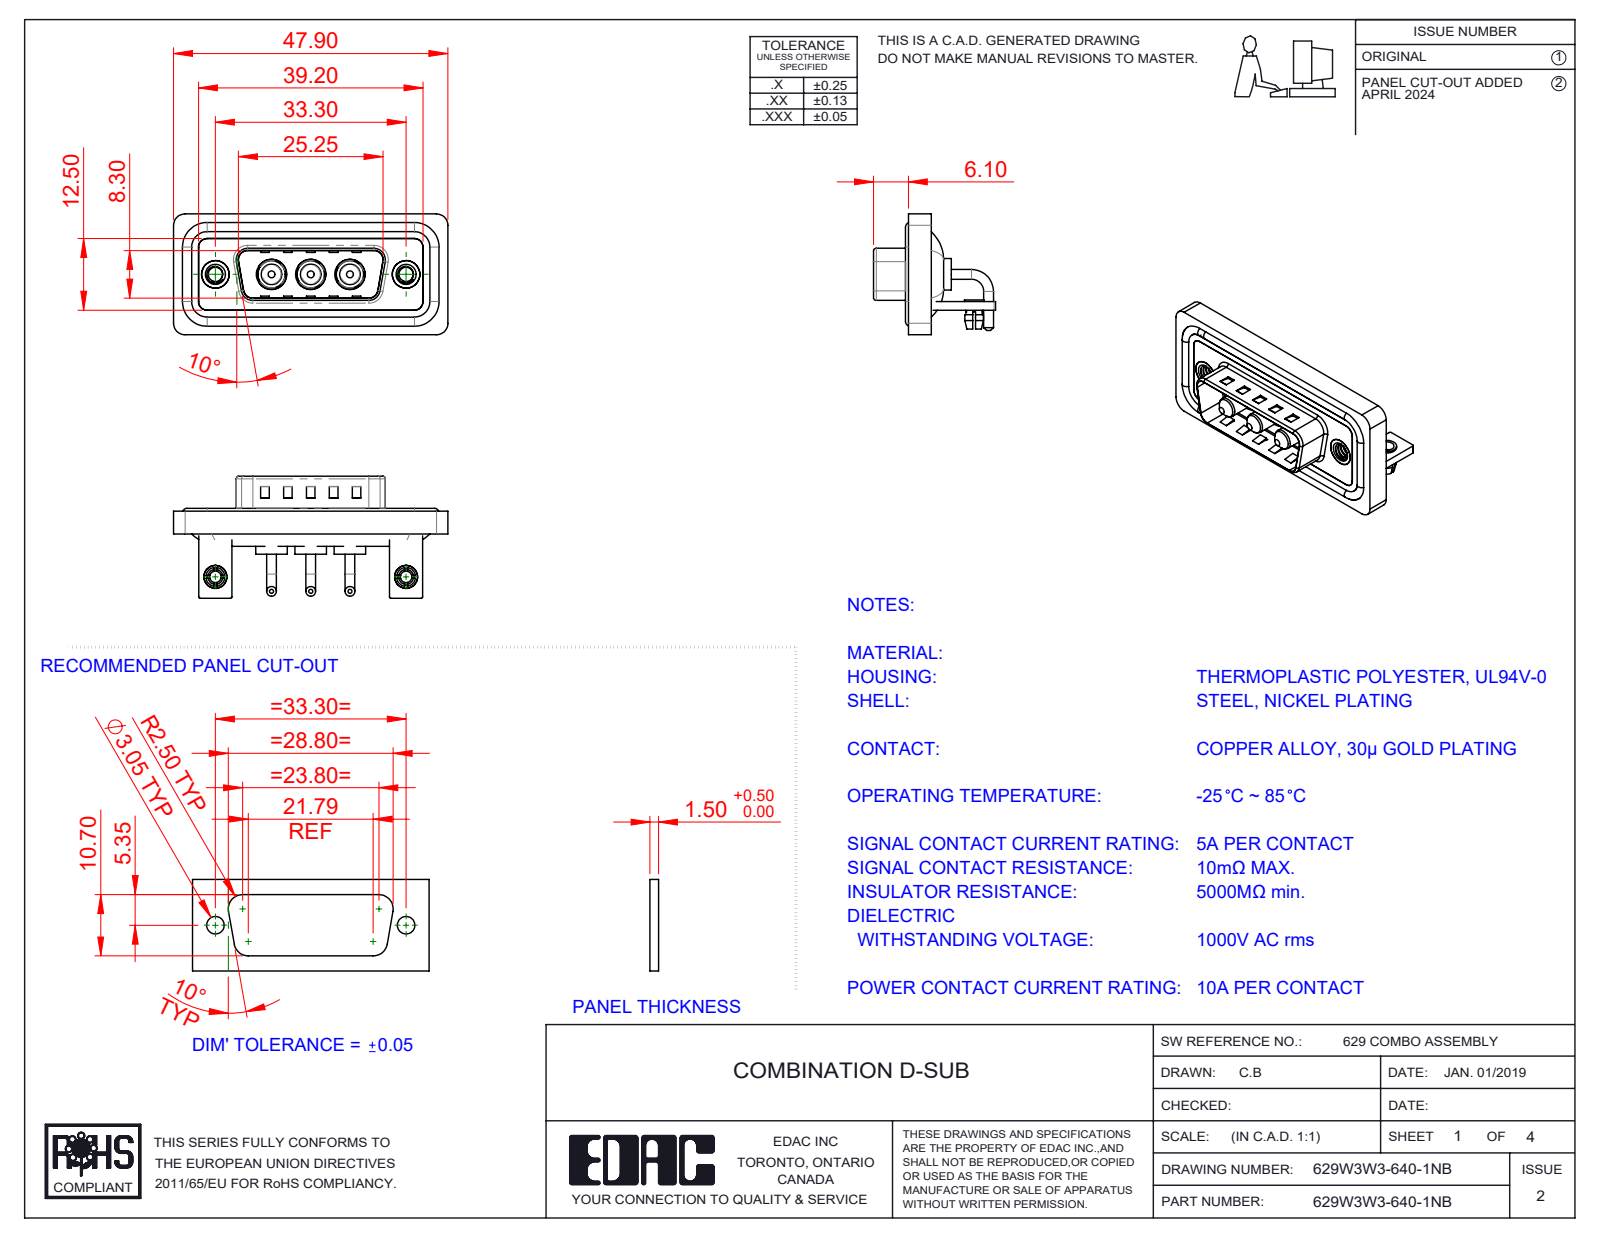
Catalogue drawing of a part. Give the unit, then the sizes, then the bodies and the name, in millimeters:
Units: millimetres
Overall size (bounding box): 47.9 × 21.3 × 21.1
Round holes (diameter × count): ⌀2.5 ×4, ⌀4.85 ×3, ⌀5.3 ×3, ⌀2 ×2, ⌀3.2 ×2, ⌀4 ×2, ⌀4.8 ×2, ⌀5 ×2
Round bosses / shafts (diameter × count): ⌀1.7 ×6, ⌀1.6 ×4, ⌀5.5 ×3, ⌀5.2 ×3, ⌀4.75 ×3, ⌀3.75 ×3, ⌀3.6 ×3, ⌀4.9 ×2
Partial cylindrical surfaces — rounded edges, fillets, slot ends (radius × count): R2 ×21, R1.5 ×18, R0.25 ×16, R0.5 ×9, R1.6 ×8, R0.6 ×4, R0.65 ×4, R0.9 ×4
Main face-to-face distances: 0.4, 1.5, 0.8, 2.9, 1.1, 2.1, 3.7, 1.6, 1.2, 4.5
Hole centre spacings: 6.85, 9.8, 16.65, 23.5, 33.3, 13.7
Volume: 5 912 mm³ · Surface area: 9 682 mm²
Bodies: 17 solids, 706 faces (275 planar, 297 cylindrical, 134 other)
Part name (STEP PRODUCT): 629Combo Board Lock; 629Combo Threaded Rivet_B; 629Combo Housing_3W3; 629Combo Shell Rear_15 Contacts (+5 more)
STEP written by: SolidWorks 2023 (CONFIG_CONTROL_DESIGN)
